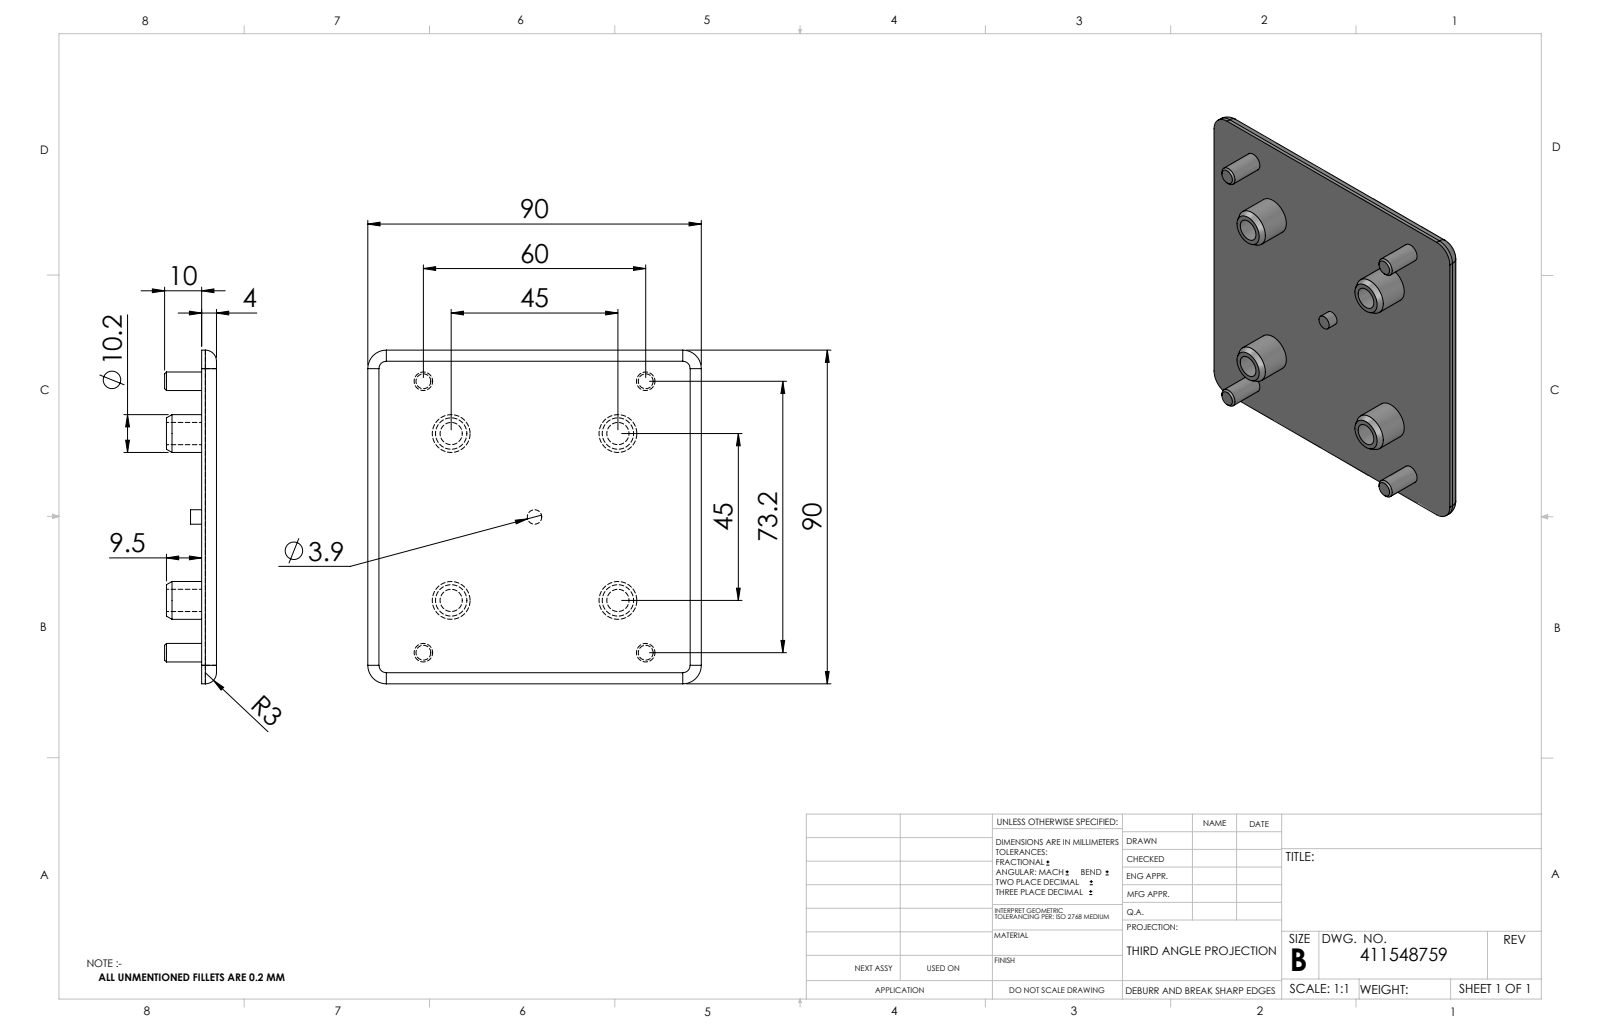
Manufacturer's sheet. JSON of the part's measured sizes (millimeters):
{"part_name": "411548759", "step_written_by": "SolidWorks 2014 (CONFIG_CONTROL_DESIGN)", "units": "millimeters", "bodies": {"solids": 1, "faces": 73, "planar": 19, "cylindrical": 34, "other": 20}, "overall_size": [90, 90, 14], "volume_mm3": 34411, "surface_area_mm2": 19595, "round_holes": [[6, 4]], "round_bosses_or_shafts": [[10.2, 4], [5, 4], [3.9, 1]], "partial_cylinders_radius": [[3, 4], [5, 4]], "face_to_face_distances": [4, 90, 9.5, 13.5, 0.5, 10, 14, 7, 6.5, 3], "hole_center_spacings": [45, 63.64]}
